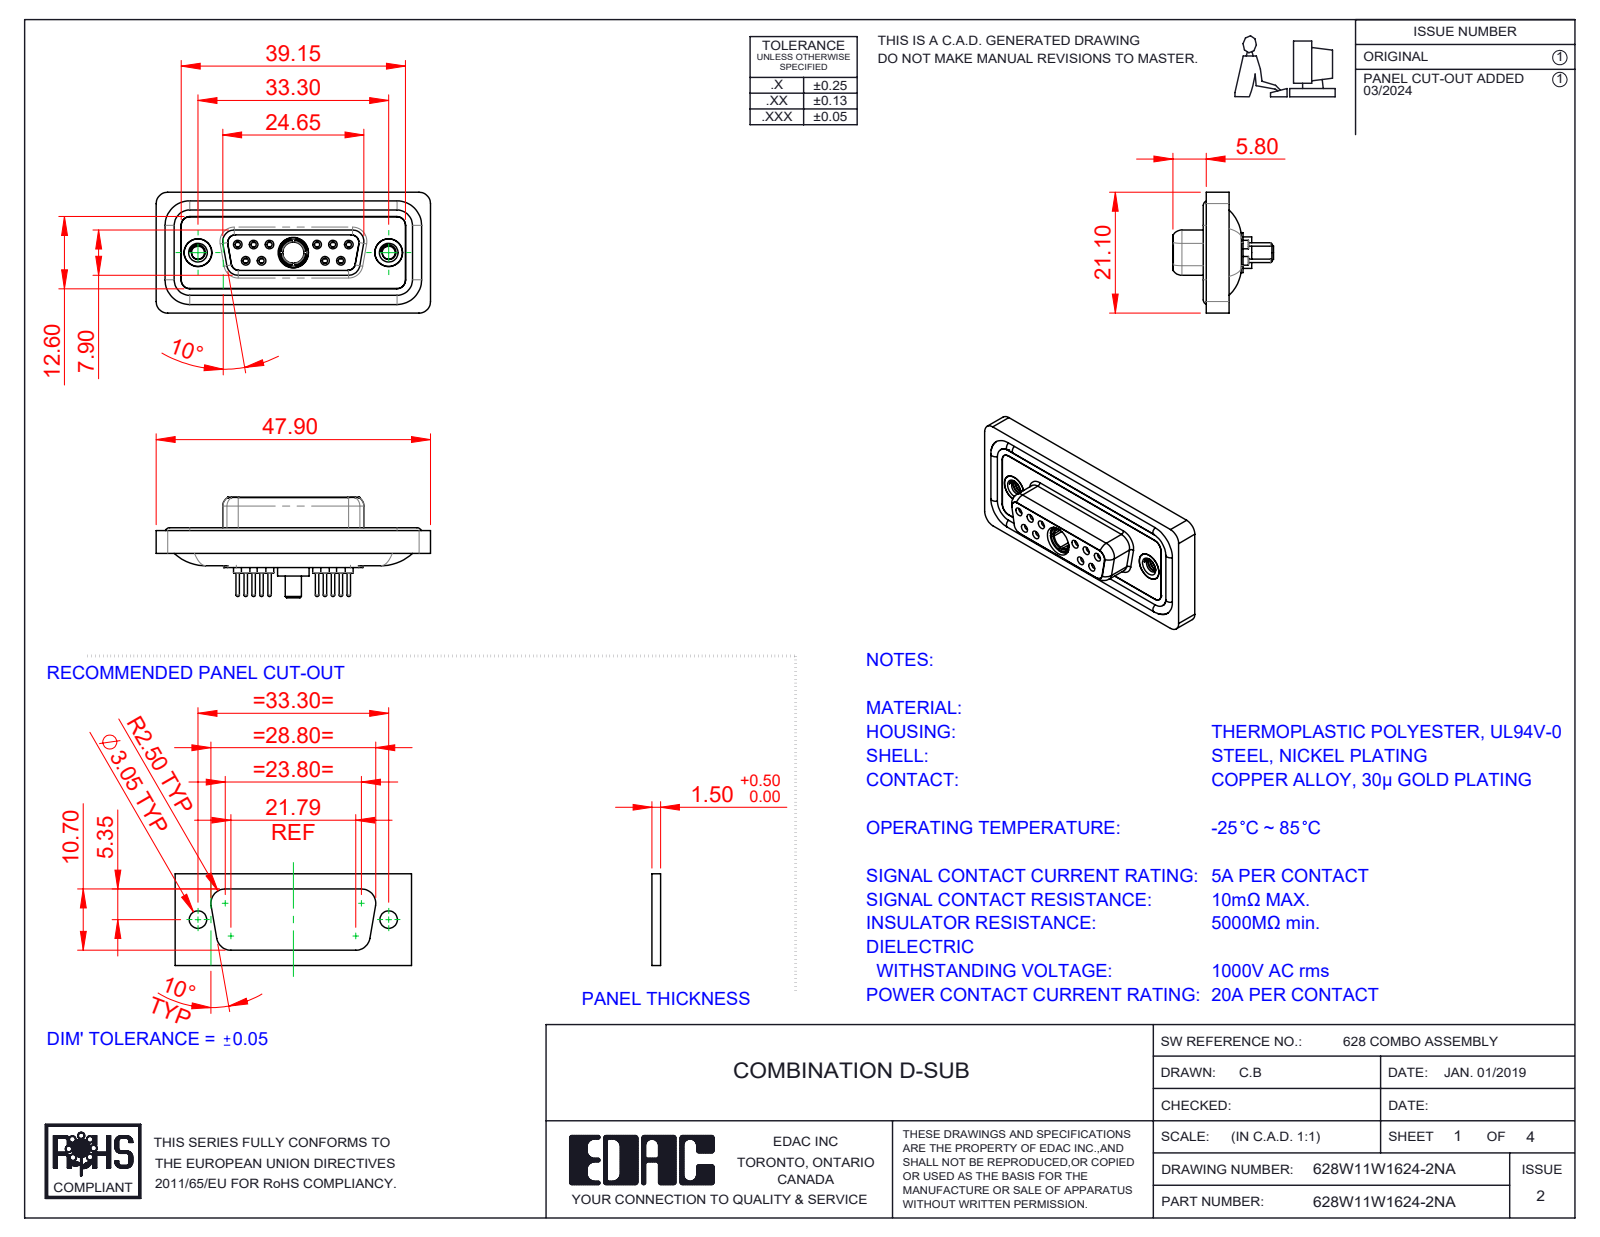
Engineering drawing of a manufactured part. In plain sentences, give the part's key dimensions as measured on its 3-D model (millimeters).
The part is named "628Combo Shell Rear_15 Contacts; 628Combo Housing_11W1; 628Combo Waterproof Housing_15 Contacts; 628Combo Contact Row 1_24 (+5 more)". Its 3-D file was written by "SolidWorks 2023 (CONFIG_CONTROL_DESIGN)". It is 19 solids with 1008 faces: 284 planar, 403 cylindrical and 321 other. Overall it measures 47.9 by 21.1 by 17.55 millimeters. Its volume is 6 128 cubic millimeters and its surface area 10 030 square millimeters. Round holes: 10 of diameter 0.9, 10 of diameter 1.1, 10 of diameter 1.5, 10 of diameter 2, 6 of diameter 1.7, 4 of diameter 1.6, 3 of diameter 4.85, 2 of diameter 2.26, 2 of diameter 4, 2 of diameter 4.05, 2 of diameter 5, 1 of diameter 3.7. Round bosses or shafts: 10 of diameter 2.2, 10 of diameter 1.6, 10 of diameter 0.6, 2 of diameter 4.95, 2 of diameter 4.8, 1 of diameter 5.5, 1 of diameter 5.2, 1 of diameter 4.96. Partial cylindrical surfaces (rounded edges, fillets, slot ends): 22 of radius 1.5, 20 of radius 2, 12 of radius 1.35, 8 of radius 1.6, 4 of radius 0.25, 4 of radius 0.5, 4 of radius 0.6, 4 of radius 0.65. The main face-to-face distances are 0.4, 1.6, 1.8, 2.9, 0.5, 1.1, 5.65, 7.45, 6.6, 7.05. The hole center spacings are 3.16, 2.77, 13.85, 11.08, 16.62, 5.03, 5.04, 5.54.
